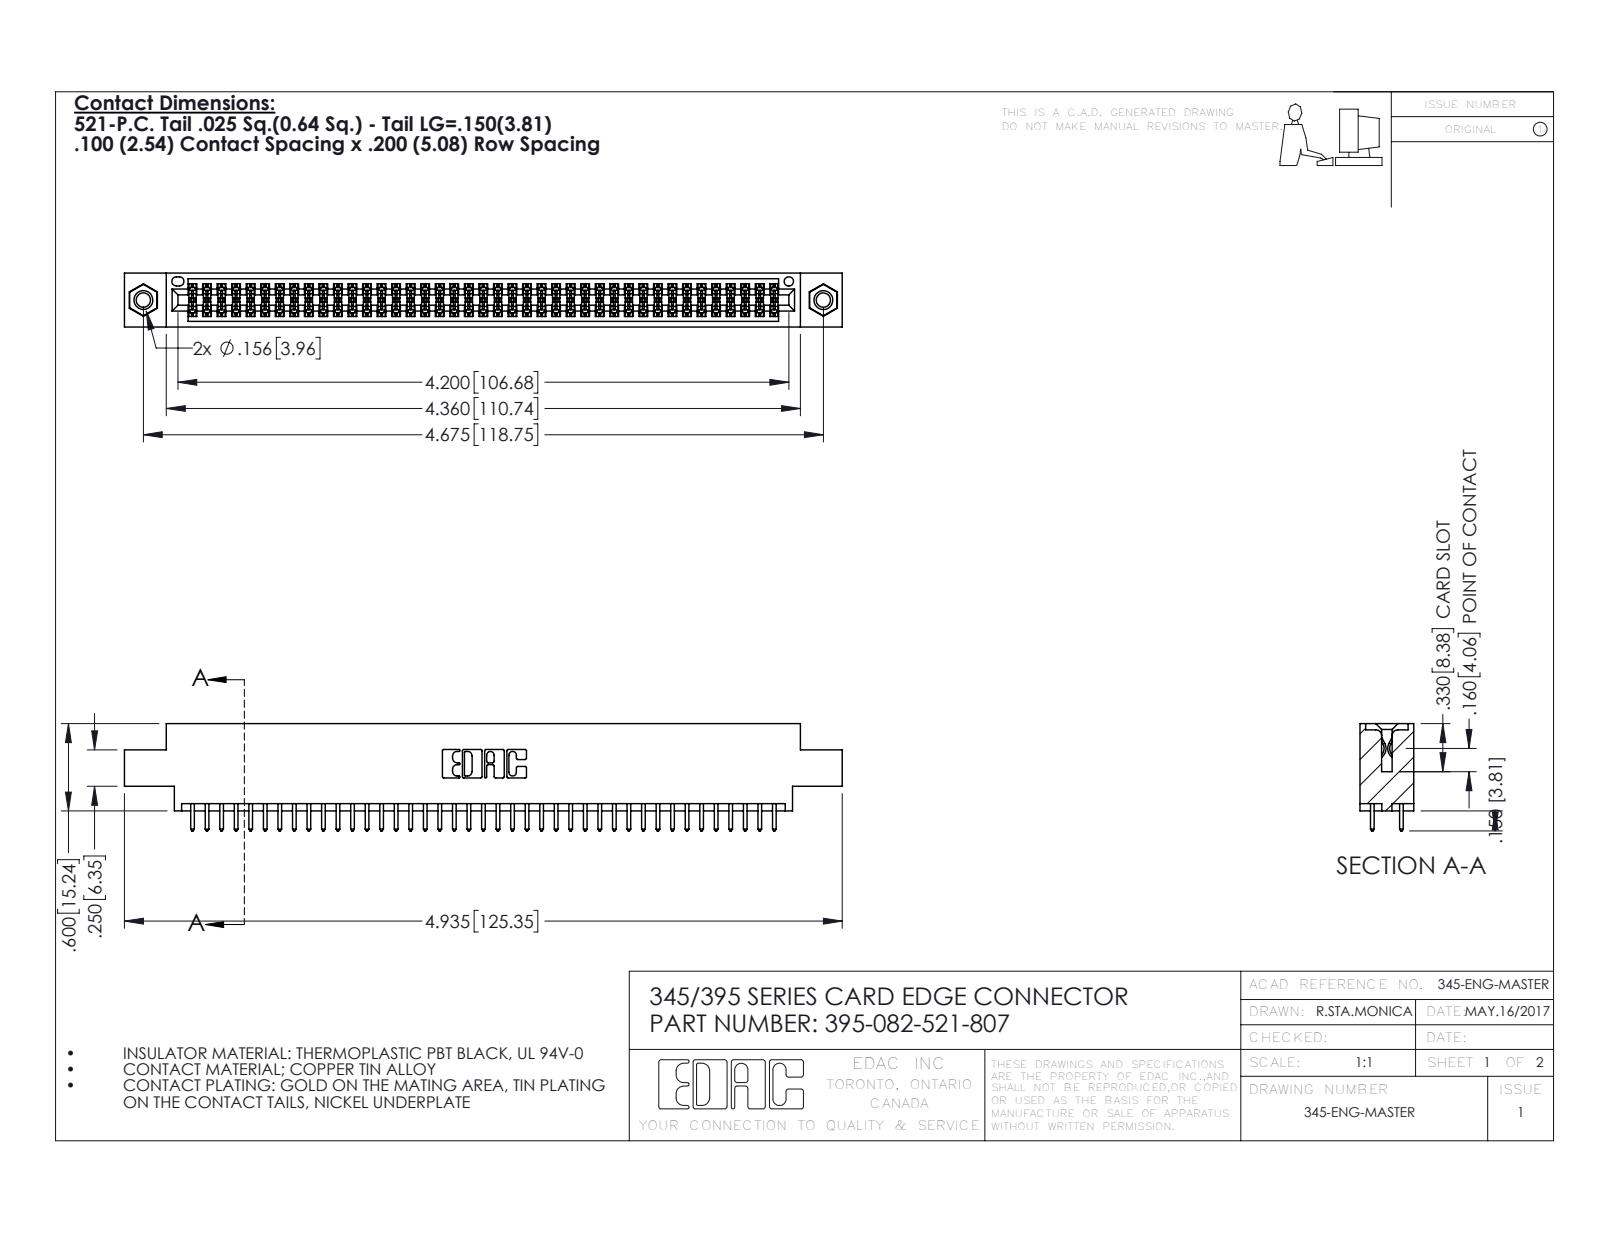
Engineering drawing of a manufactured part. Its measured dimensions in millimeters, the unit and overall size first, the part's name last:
Units: millimetres
Overall size (bounding box): 125.3 × 18.7 × 9.4
Round holes (diameter × count): ⌀2.5 ×2, ⌀3.2 ×2, ⌀4 ×2, ⌀1.6 ×1
Round bosses / shafts (diameter × count): ⌀3.9 ×2
Partial cylindrical surfaces — rounded edges, fillets, slot ends (radius × count): R0.2 ×123, R0.3 ×82, R0.3 ×22, R0.2 ×6, R0.8 ×6, R0.7 ×3, R0.4 ×2, R0.5 ×2
Main face-to-face distances: 1.8, 7.6, 9.4, 5.1, 2.5, 6.9, 0.6, 5.7, 4.4, 3.8
Hole centre spacings: 6.9, 112.8, 118.7
Volume: 12 000 mm³ · Surface area: 17 680 mm²
Bodies: 85 solids, 4290 faces (2822 planar, 1452 cylindrical, 16 other)
Part name (STEP PRODUCT): 345 Part_0.170 Offset - 0.156 Dia-TI; 345-292-001_345-293-121; 345-250-001_345-250-005-103; 395-082-521-807
STEP written by: SolidWorks 2016 (CONFIG_CONTROL_DESIGN)
